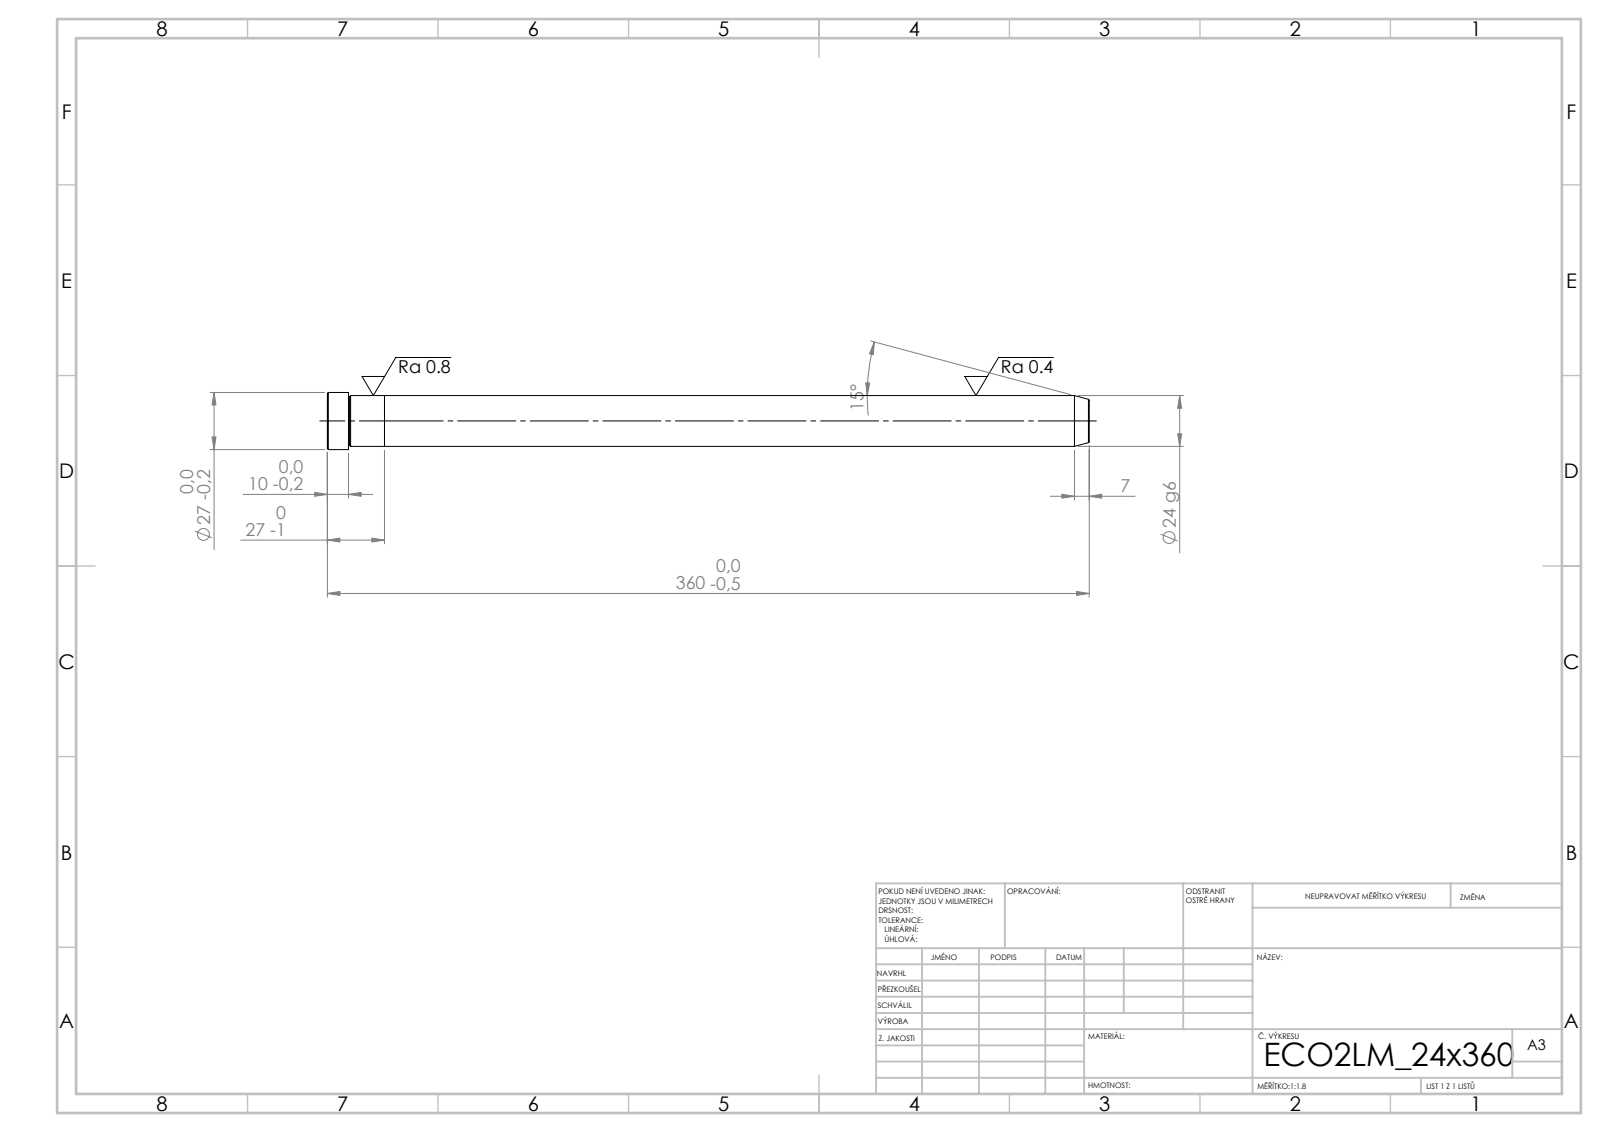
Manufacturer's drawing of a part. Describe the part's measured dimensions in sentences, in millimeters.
Its 3-D file was written by "SolidWorks 2019 (CONFIG_CONTROL_DESIGN)". It is 2 solids with 21 faces: 5 planar, 6 cylindrical and 10 other. Overall it measures 360 by 27 by 27 millimeters. Its volume is 163 551 cubic millimeters and its surface area 29 141 square millimeters. Round bosses or shafts: 1 of diameter 27, 1 of diameter 24. The main face-to-face distances are 27, 333, 360, 350, 17, 10.
